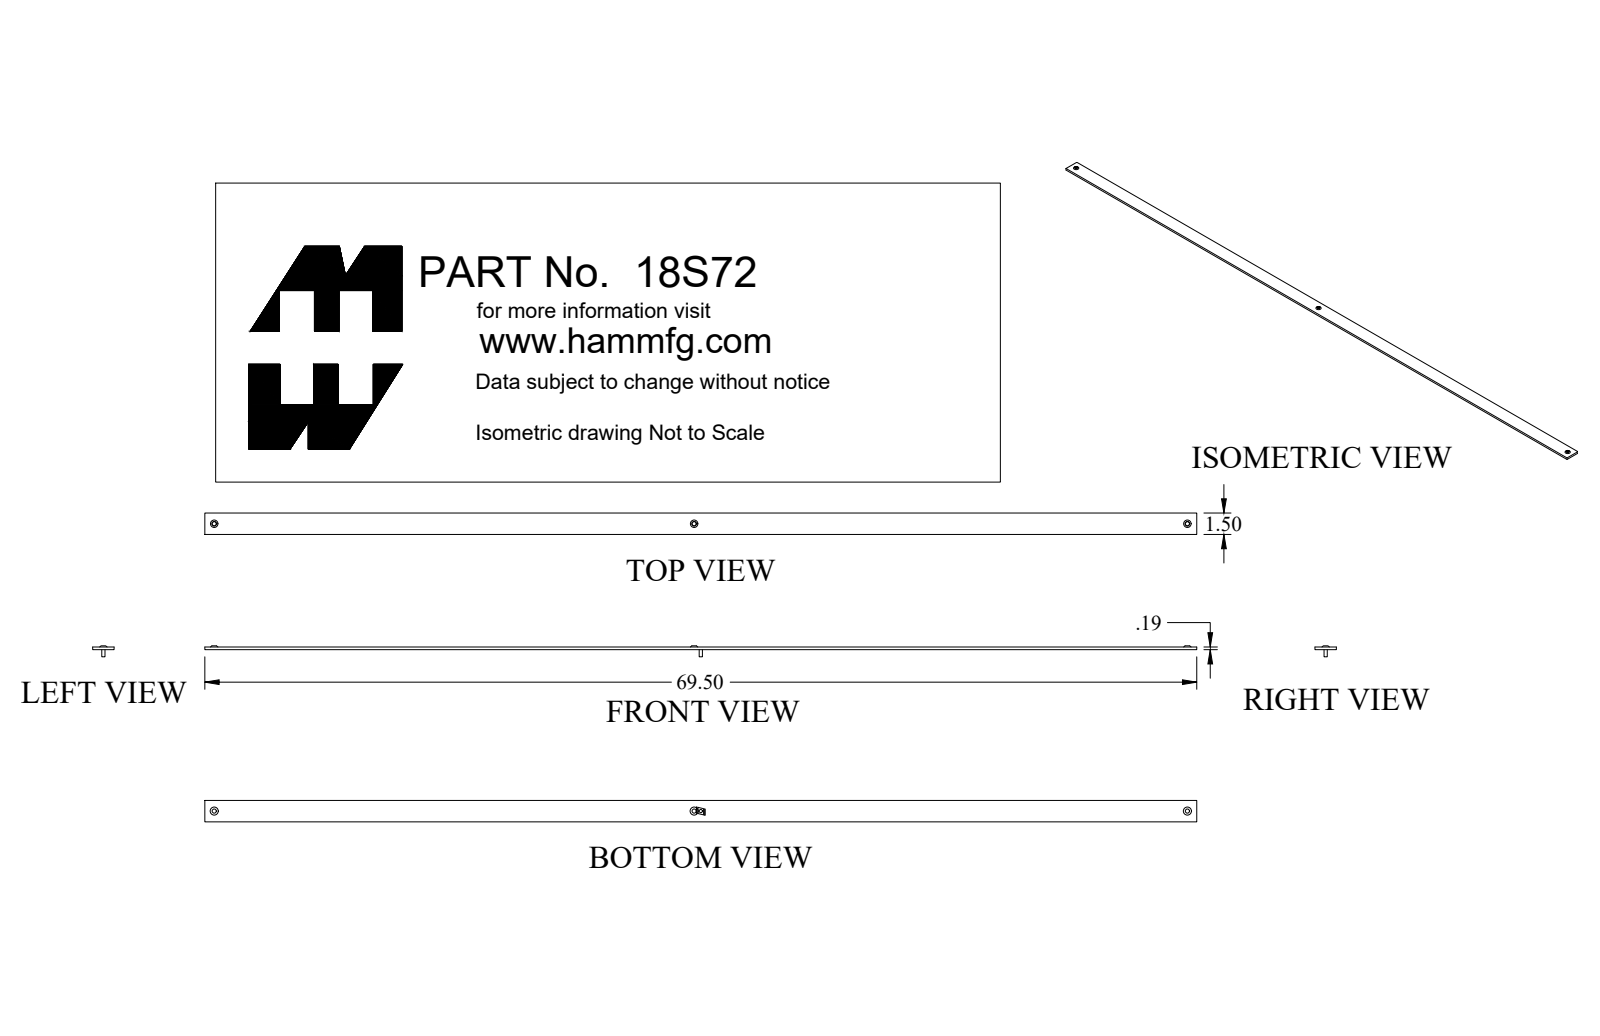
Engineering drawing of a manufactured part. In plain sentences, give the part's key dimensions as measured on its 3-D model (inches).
The part is named "18S72_Default". Its 3-D file was written by "SolidWorks 2018 (CONFIG_CONTROL_DESIGN)". It is 1 solid with 27 faces: 9 planar, 6 cylindrical and 12 other. Overall it measures 69.5 by 1.5 by 0.27 inches. Its volume is 19.54 cubic inches and its surface area 235.5 square inches. Round holes: 3 of diameter 0.296. The main face-to-face distances are 0.188, 1.5, 69.5, 0.27, 0.082. The hole center spacings are 33.625, 34.563, 68.188.
